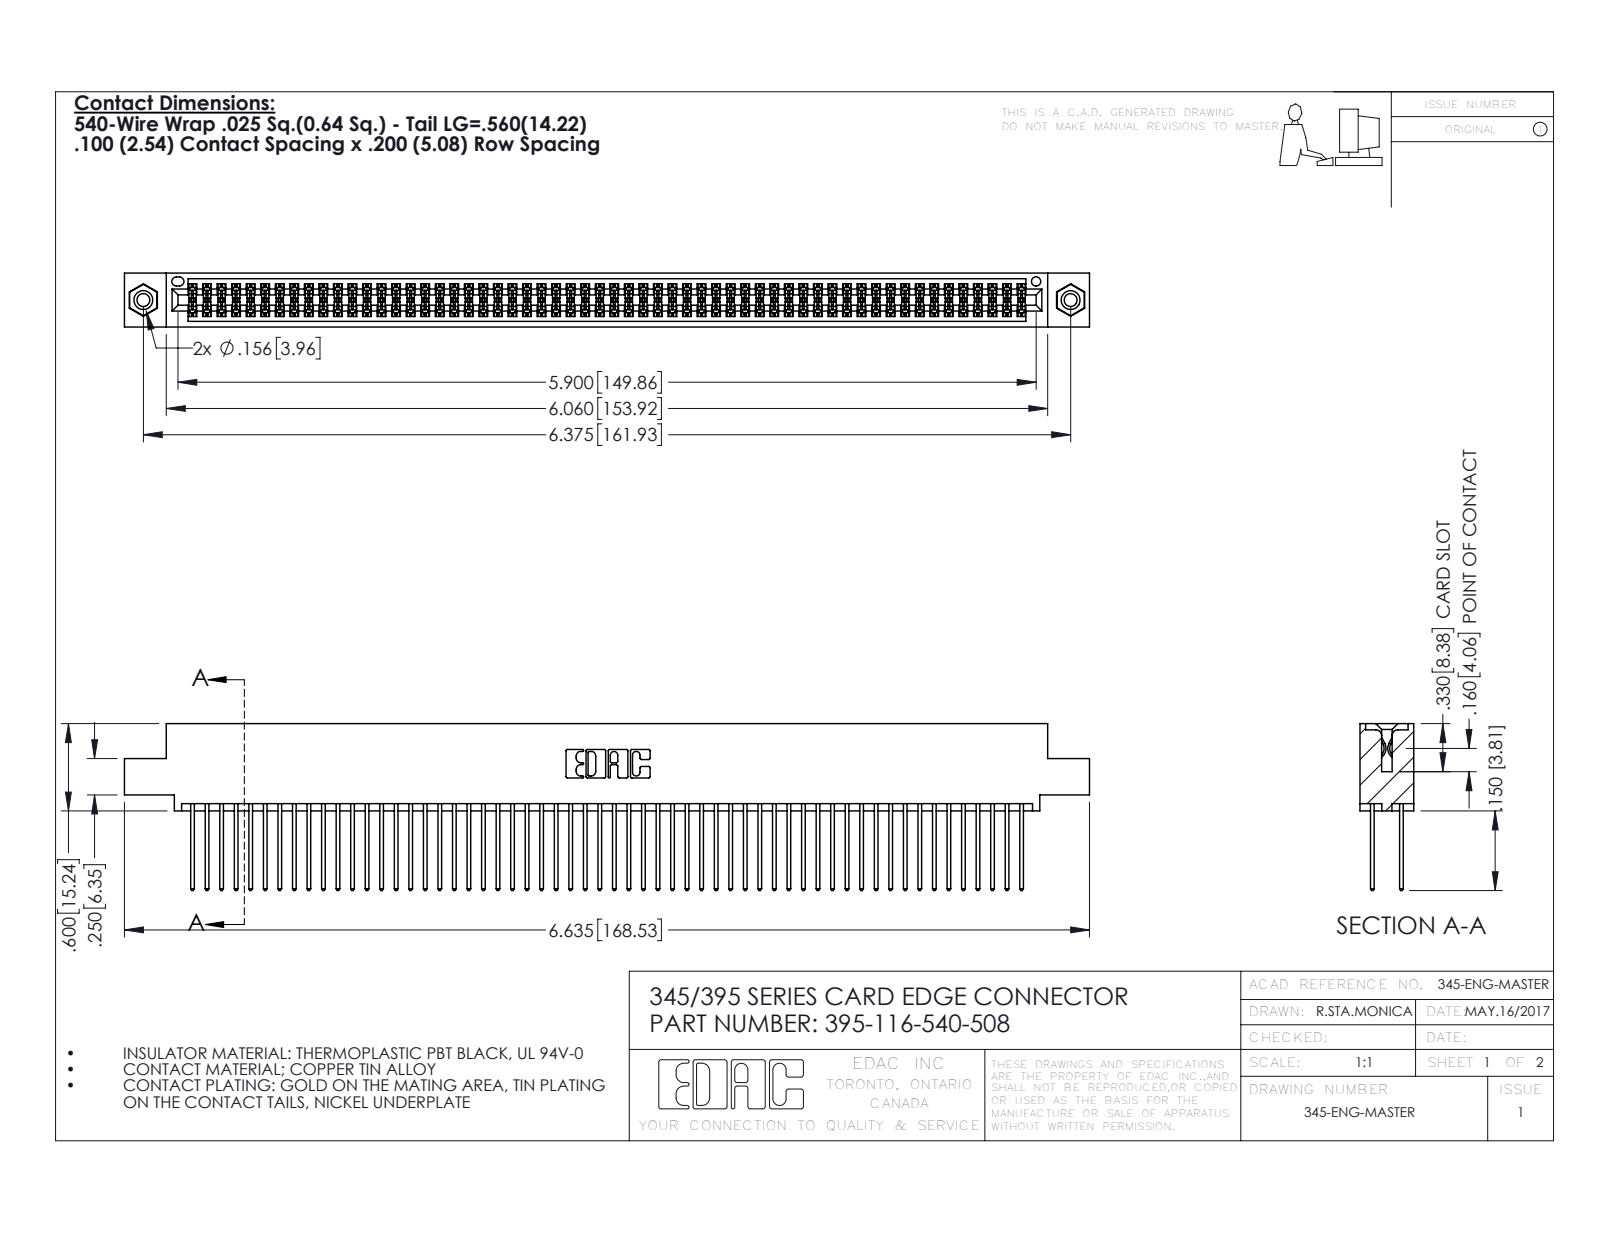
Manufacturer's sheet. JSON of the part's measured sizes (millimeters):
{"part_name": "395-116-540-508; 345 Part_0.110 Offset - 0.156 Dia-TI; 345-292-001_345-293-140; 345-250-001_345-250-003-102", "step_written_by": "SolidWorks 2016 (CONFIG_CONTROL_DESIGN)", "units": "millimeters", "bodies": {"solids": 119, "faces": 5990, "planar": 3944, "cylindrical": 2030, "other": 16}, "overall_size": [168.5, 29.1, 9.4], "volume_mm3": 16880, "surface_area_mm2": 27410, "round_holes": [[2.3, 2], [3.2, 2], [4, 2], [1.6, 1]], "round_bosses_or_shafts": [[3.9, 2]], "partial_cylinders_radius": [[0.2, 174], [0.3, 116], [0.3, 22], [0.2, 6], [0.8, 6], [0.7, 3], [0.4, 2], [0.5, 2]], "face_to_face_distances": [1.8, 7.6, 5.1, 2.5, 6.9, 0.6, 9.4, 5.7, 4.4, 3.8], "hole_center_spacings": [6.9, 155.9, 161.9]}
